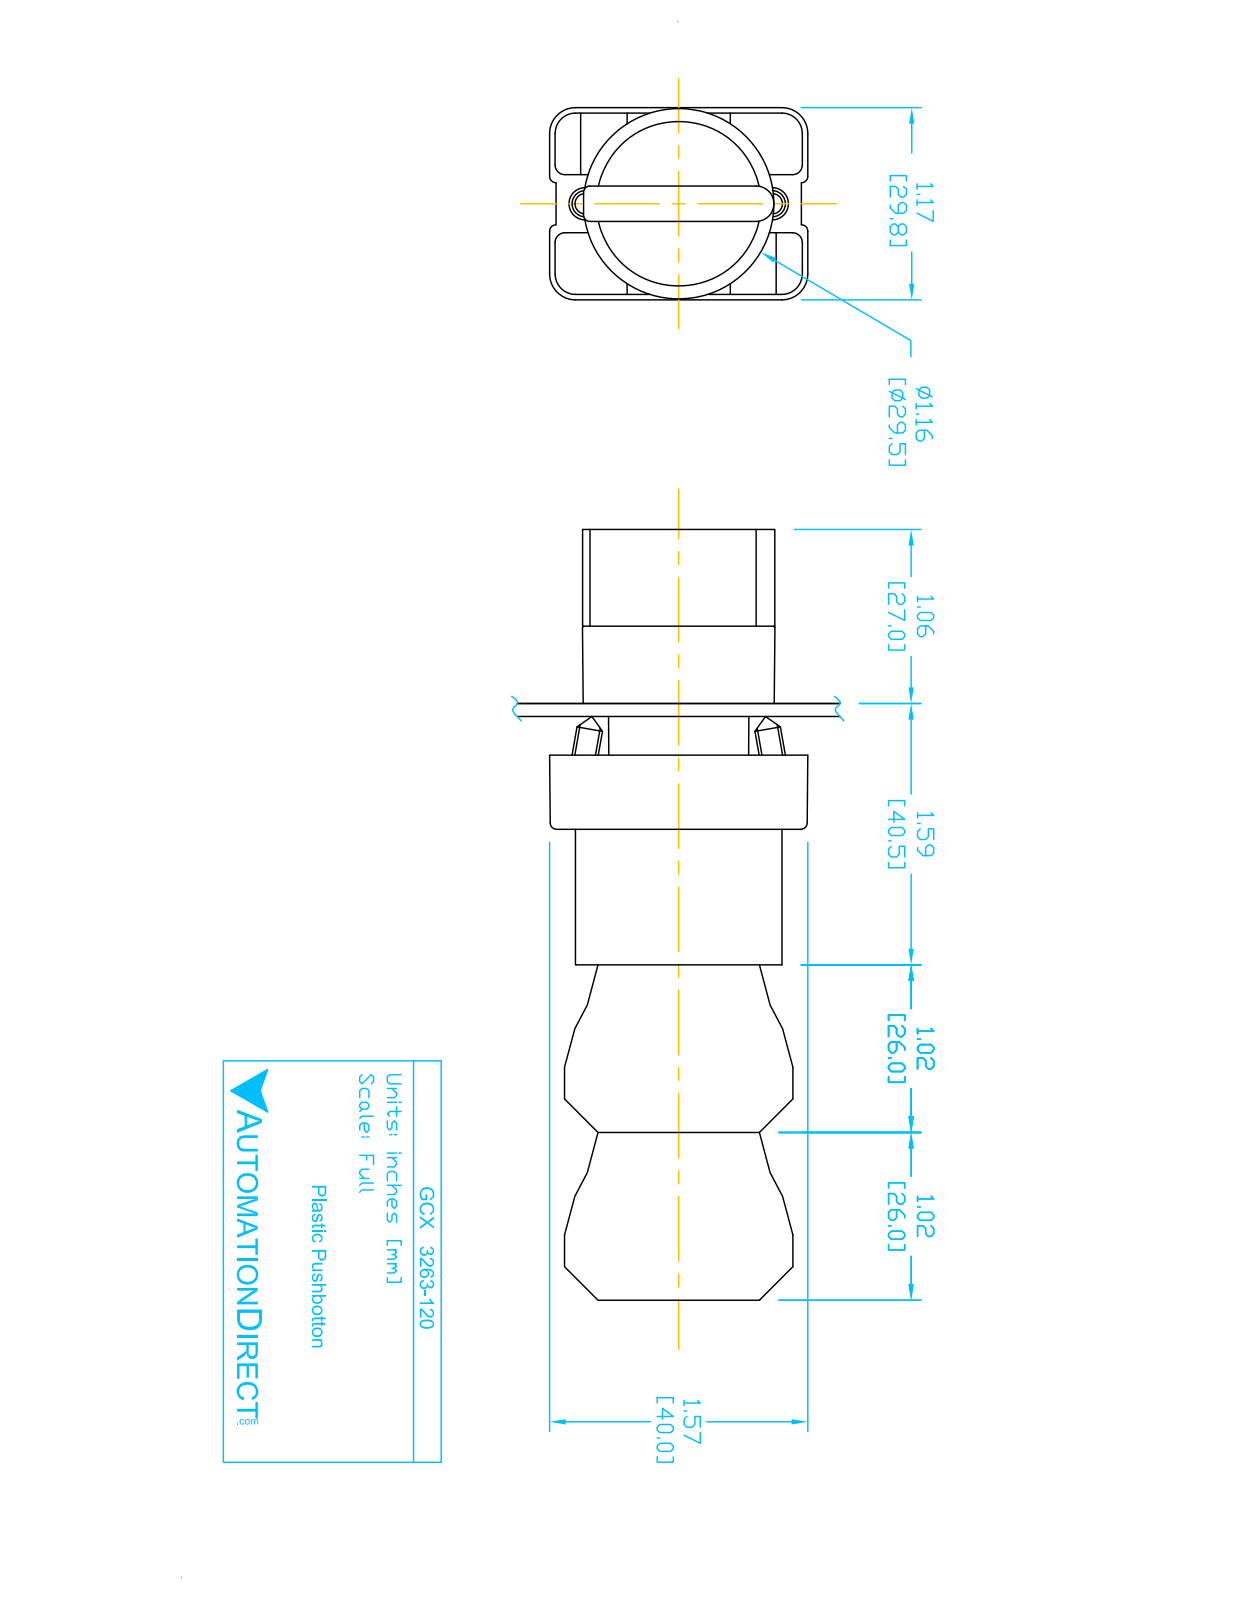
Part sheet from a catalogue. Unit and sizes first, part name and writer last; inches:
Units: inches
Overall size (bounding box): 4.677 × 1.581 × 1.177
Round holes (diameter × count): ⌀0.079 ×4, ⌀0.087 ×2, ⌀0.124 ×2, ⌀0.13 ×2, ⌀0.197 ×1, ⌀0.469 ×1, ⌀0.878 ×1, ⌀0.888 ×1, ⌀1.024 ×1
Round bosses / shafts (diameter × count): ⌀0.157 ×4, ⌀1.175 ×1, ⌀1.004 ×1, ⌀0.945 ×1, ⌀0.856 ×1, ⌀0.78 ×1, ⌀0.504 ×1
Partial cylindrical surfaces — rounded edges, fillets, slot ends (radius × count): R0.059 ×24, R0.041 ×12, R0.124 ×12, R0.157 ×12, R0.039 ×9, R0.02 ×2, R0.063 ×2, R0.079 ×2
Main face-to-face distances: 0.579, 0.593, 1.024, 1.171, 0.014, 0.827, 1.85, 3.043, 2.02, 1.193
Hole centre spacings: 0.236, 1.003, 0.974, 0.472, 0.539, 0.544, 1.083, 0.484
Volume: 4.751 in³ · Surface area: 59.22 in²
Bodies: 11 solids, 724 faces (488 planar, 193 cylindrical, 43 other)
Part name (STEP PRODUCT): ECX1050; ECX3029-2; GCX3263-120; GCX3263 OPERATOR (+2 more)
STEP written by: SolidWorks 2016 (AUTOMOTIVE_DESIGN)
